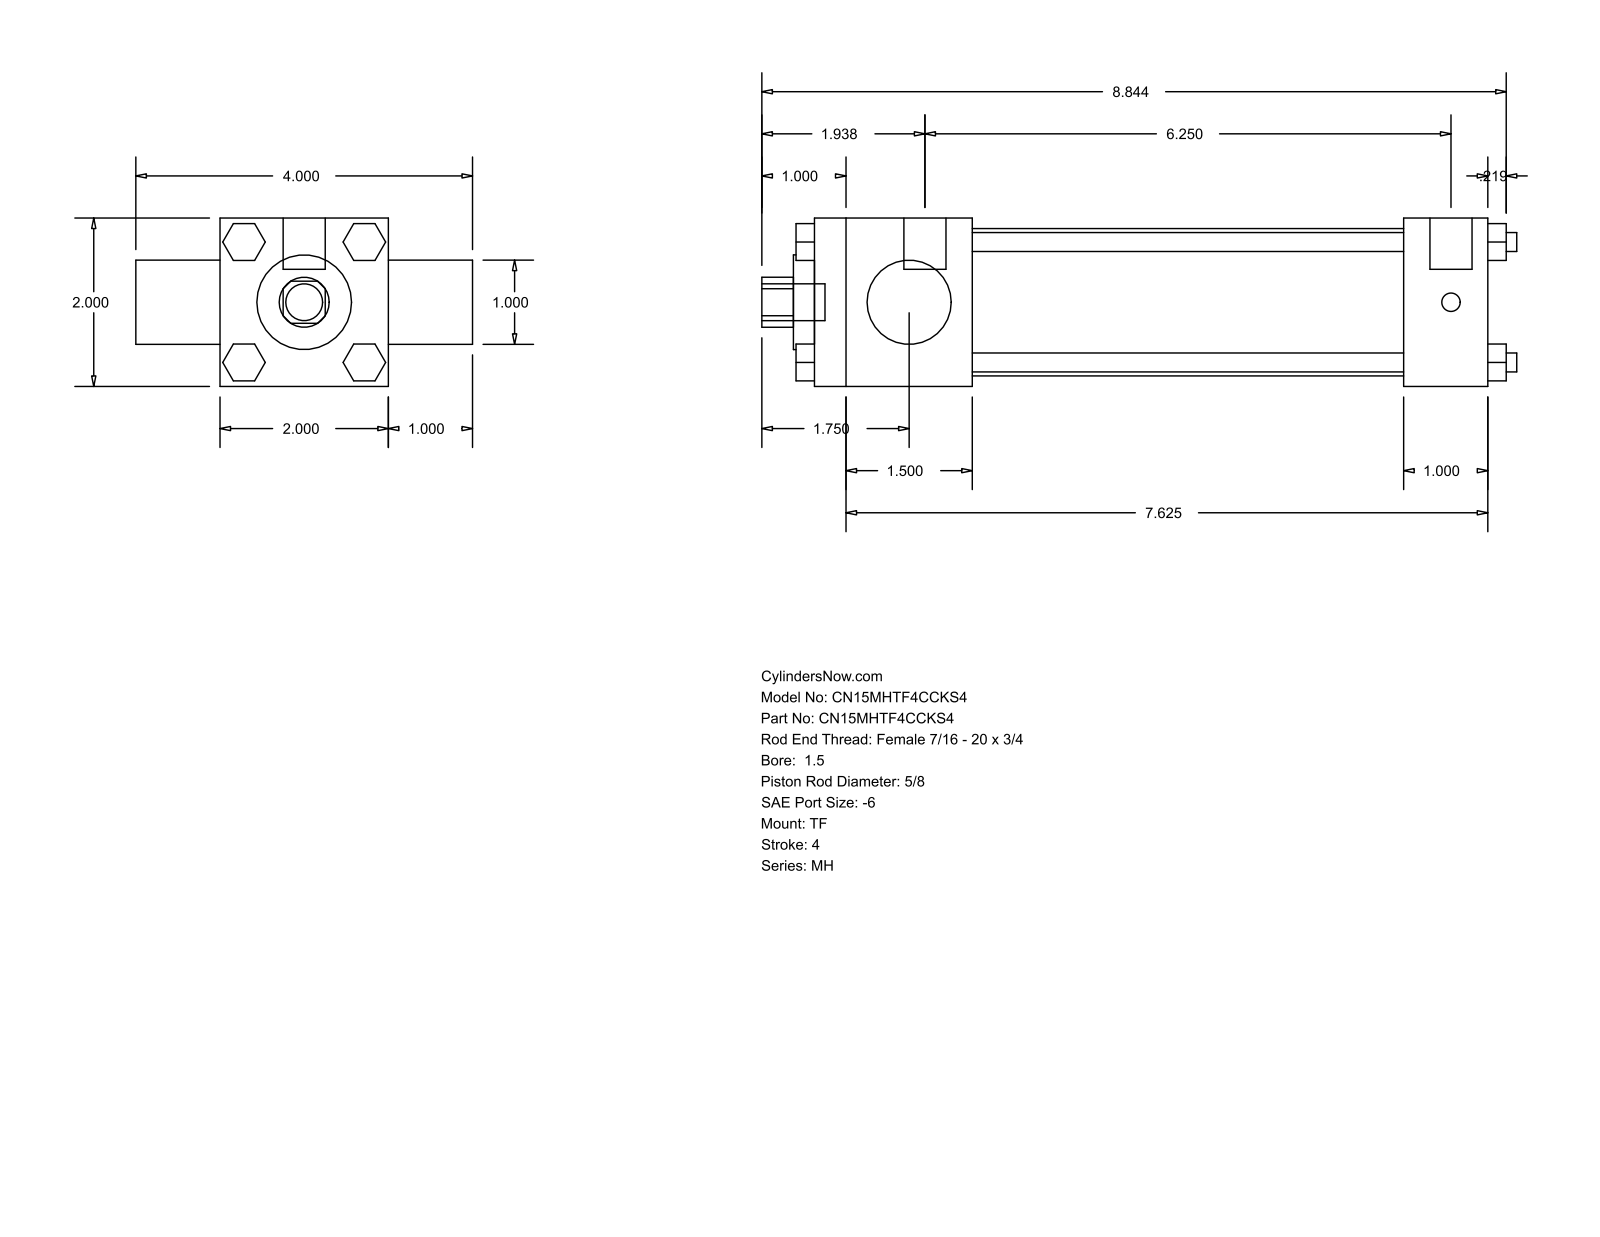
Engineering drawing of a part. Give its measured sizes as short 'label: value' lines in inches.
name: MH_TF__0150_0.625
written by: GSSL Pune (CONFIG_CONTROL_DESIGN)
unit: in
bodies: 0 solids, 120 faces (92 planar, 28 cylindrical, 0 other)
size: 8.969 × 4 × 2
holes: 1× ⌀0.625, 1× ⌀1, 1× ⌀1.125, 1× ⌀1.75
bosses: 4× ⌀0.225, 3× ⌀0.219, 2× ⌀0.5, 1× ⌀0.437
rounds: 1× R0.297
face distances: 2, 8, 1, 3, 1.875, 6.125, 7, 5.125, 1, 0.219
